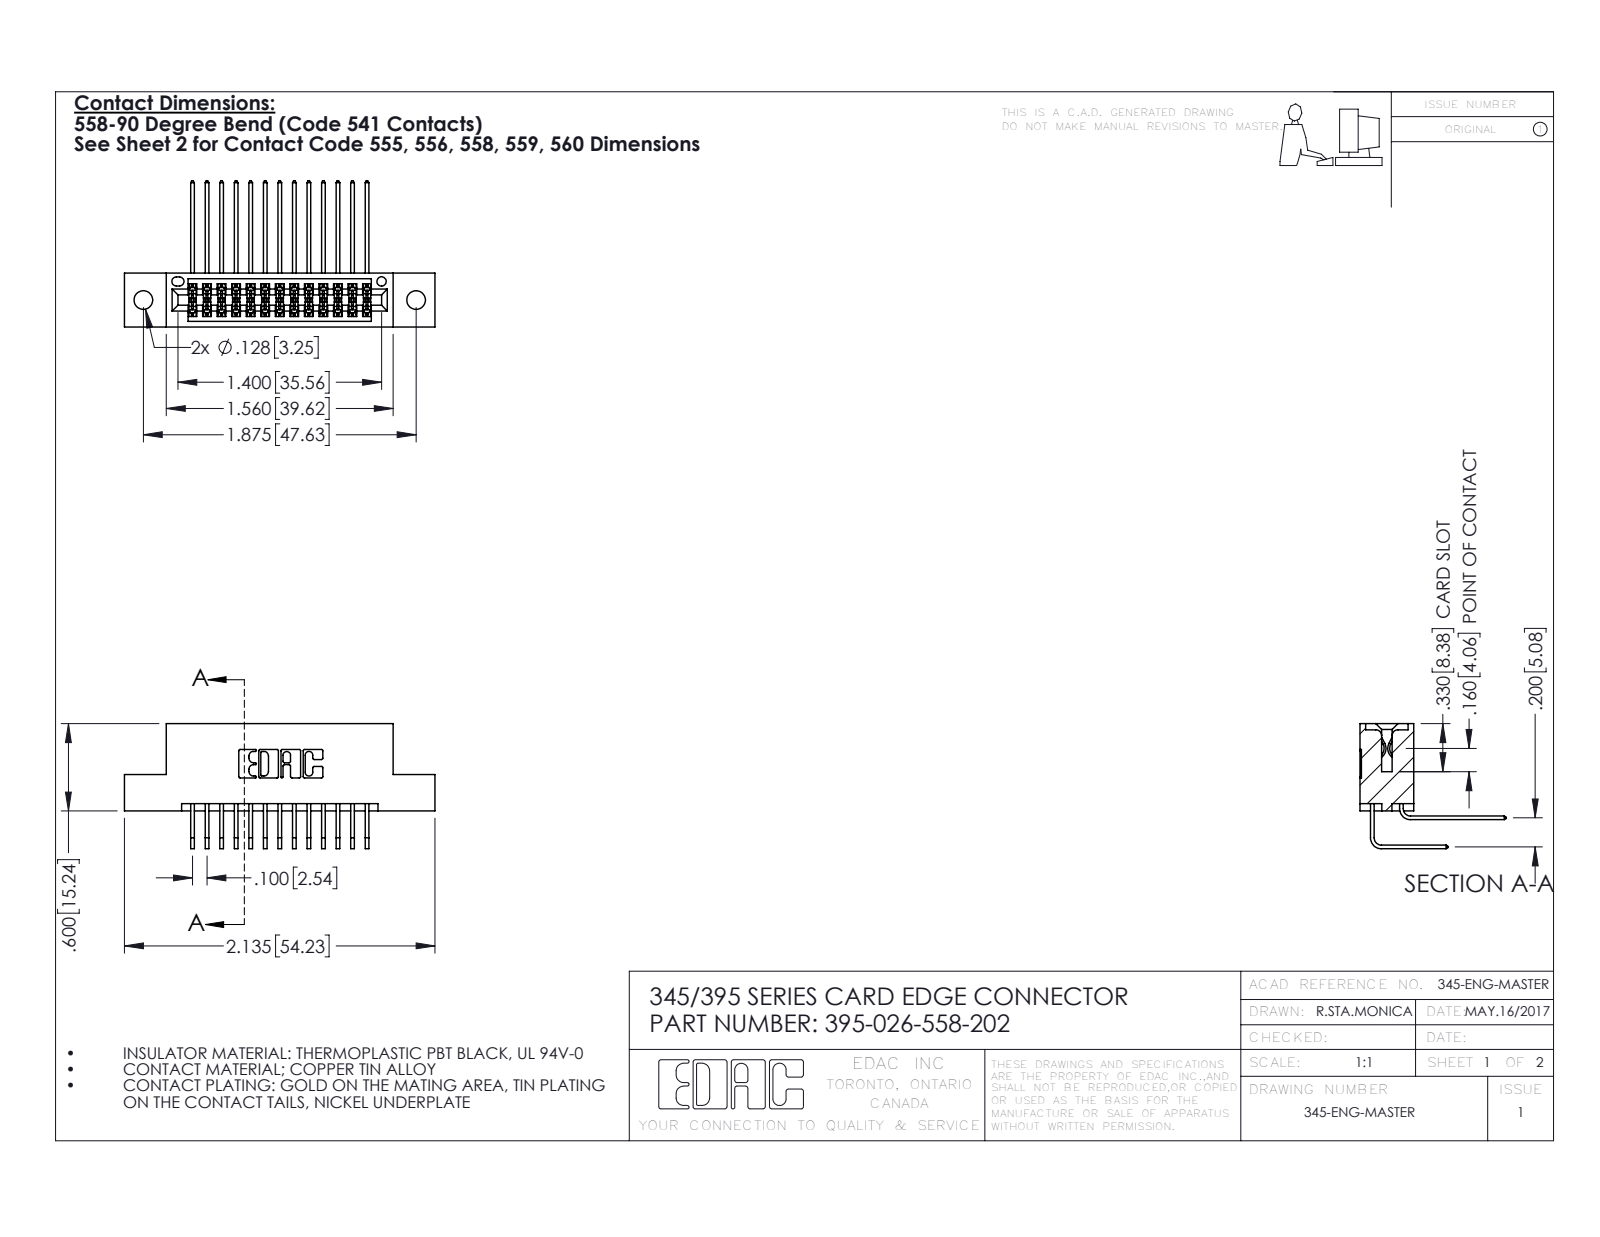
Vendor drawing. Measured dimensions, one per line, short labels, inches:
name: 345 Part_Flush Mounting Lugs - 0.128 Dia; 395-026-558-202; 345-292-001_558 Tail - 2; 345-292-001_558 559 Tail - 1
written by: SolidWorks 2016 (CONFIG_CONTROL_DESIGN)
unit: in
bodies: 27 solids, 1478 faces (990 planar, 488 cylindrical, 0 other)
size: 2.135 × 1.005 × 0.859
volume: 0.312 in³; area: 11.51 in²
holes: 2× ⌀0.128, 1× ⌀0.064
rounds: 40× R0.006, 22× R0.01, 6× R0.007, 6× R0.031, 3× R0.026, 2× R0.014, 2× R0.019, 2× R0.022
face distances: 0.2, 0.072, 0.298, 0.37, 0.098, 0.272, 0.025, 0.225, 0.1, 0.285
hole spacings: 0.27, 1.643, 1.875
